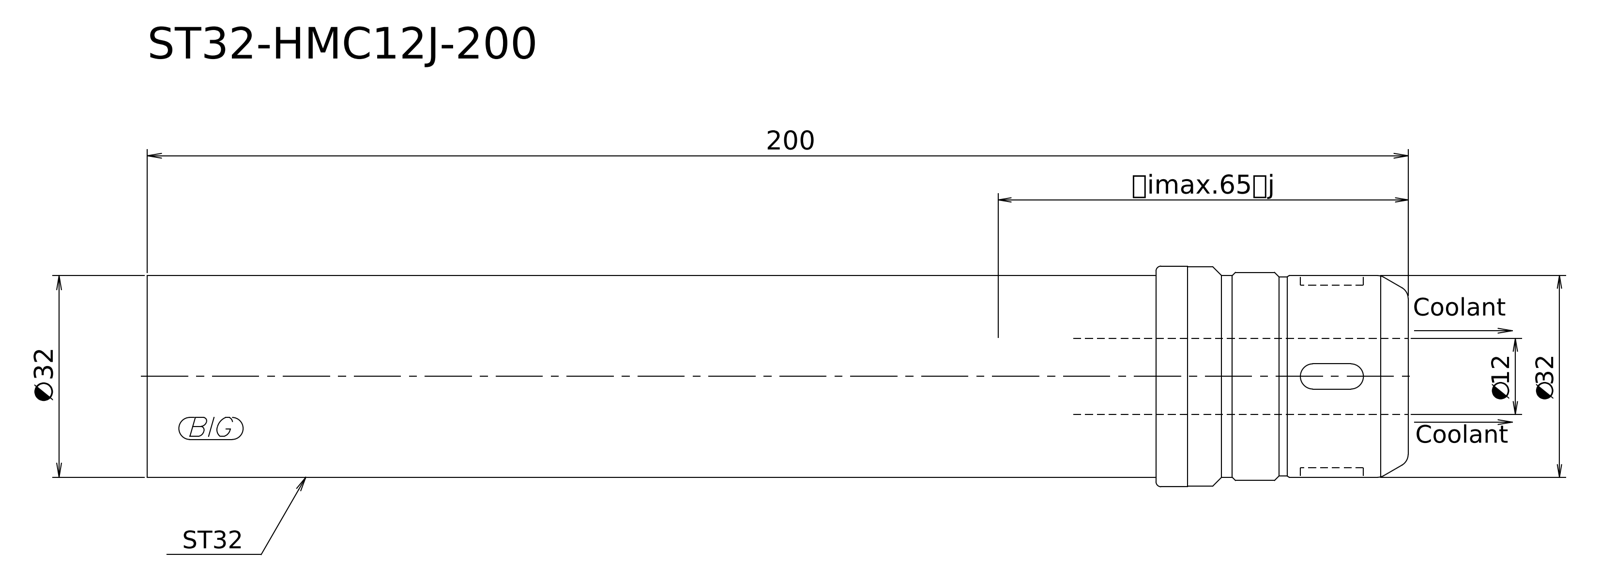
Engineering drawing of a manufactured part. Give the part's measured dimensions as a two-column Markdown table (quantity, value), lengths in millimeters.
| quantity | value |
| --- | --- |
| STEP written by | Kubotek KeyCreator 2011 V10.0.2 (22737) (automotive_design) |
| units | millimeters |
| bodies | 1 solid, 14 faces (3 planar, 6 cylindrical, 5 other) |
| overall size | 200 × 35 × 35 |
| volume | 162 166 mm³ |
| surface area | 21 900 mm² |
| round bosses / shafts (diameter × count) | 35 × 1, 33 × 1, 32 × 1, 31.6 × 1 |
| main face-to-face distances | 200, 40, 160 |
